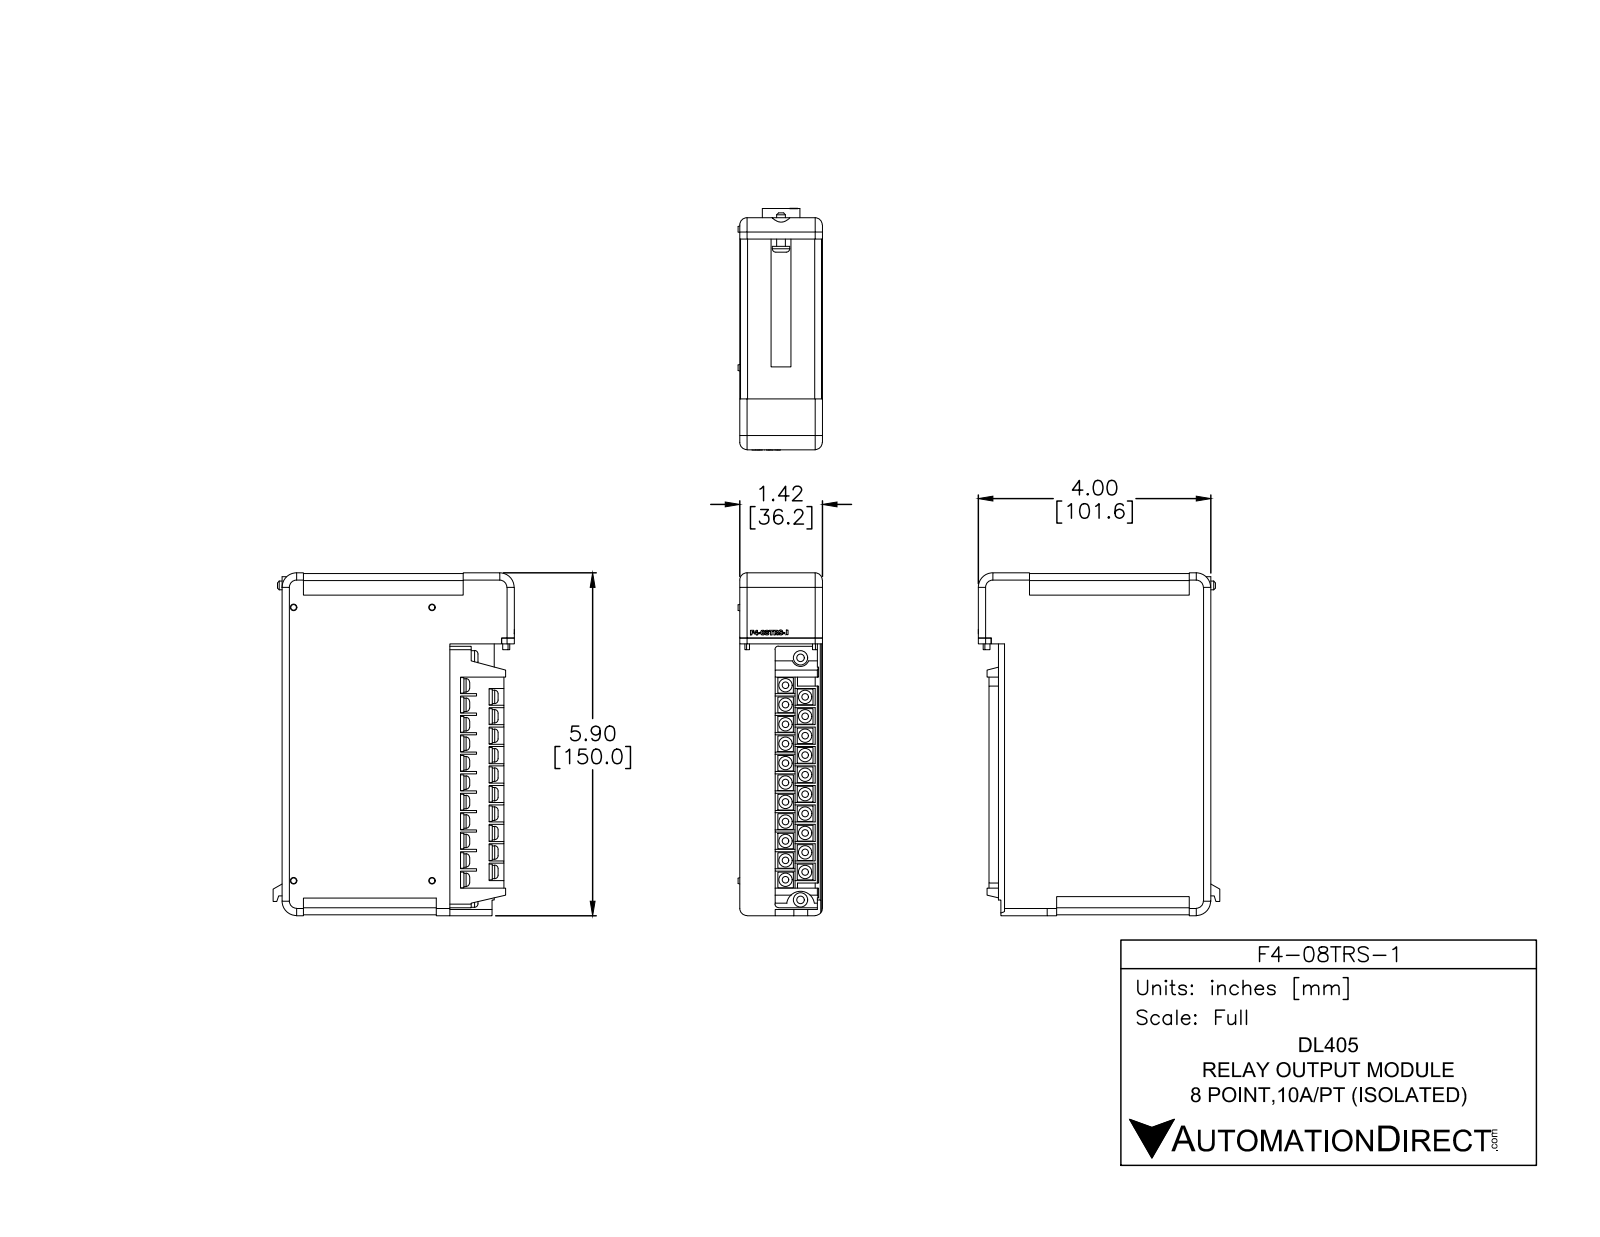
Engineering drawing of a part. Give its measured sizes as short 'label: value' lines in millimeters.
name: F4-08TRS-1
written by: SolidWorks 2014 (AUTOMOTIVE_DESIGN)
unit: mm
bodies: 16 solids, 627 faces (426 planar, 86 cylindrical, 115 other)
size: 150 × 105.6 × 37
volume: 450 800 mm³; area: 56 020 mm²
bosses: 21× ⌀5.8, 2× ⌀6.4, 1× ⌀7.6, 1× ⌀3.8
rounds: 8× R3.2, 4× R3, 3× R6.4, 2× R0.4, 2× R0.8, 2× R1.5, 1× R3.8, 1× R3.8
face distances: 36.2, 0.4, 73.4, 149.2, 35.8, 11.9, 5.1, 24.3, 149.6, 30.7
